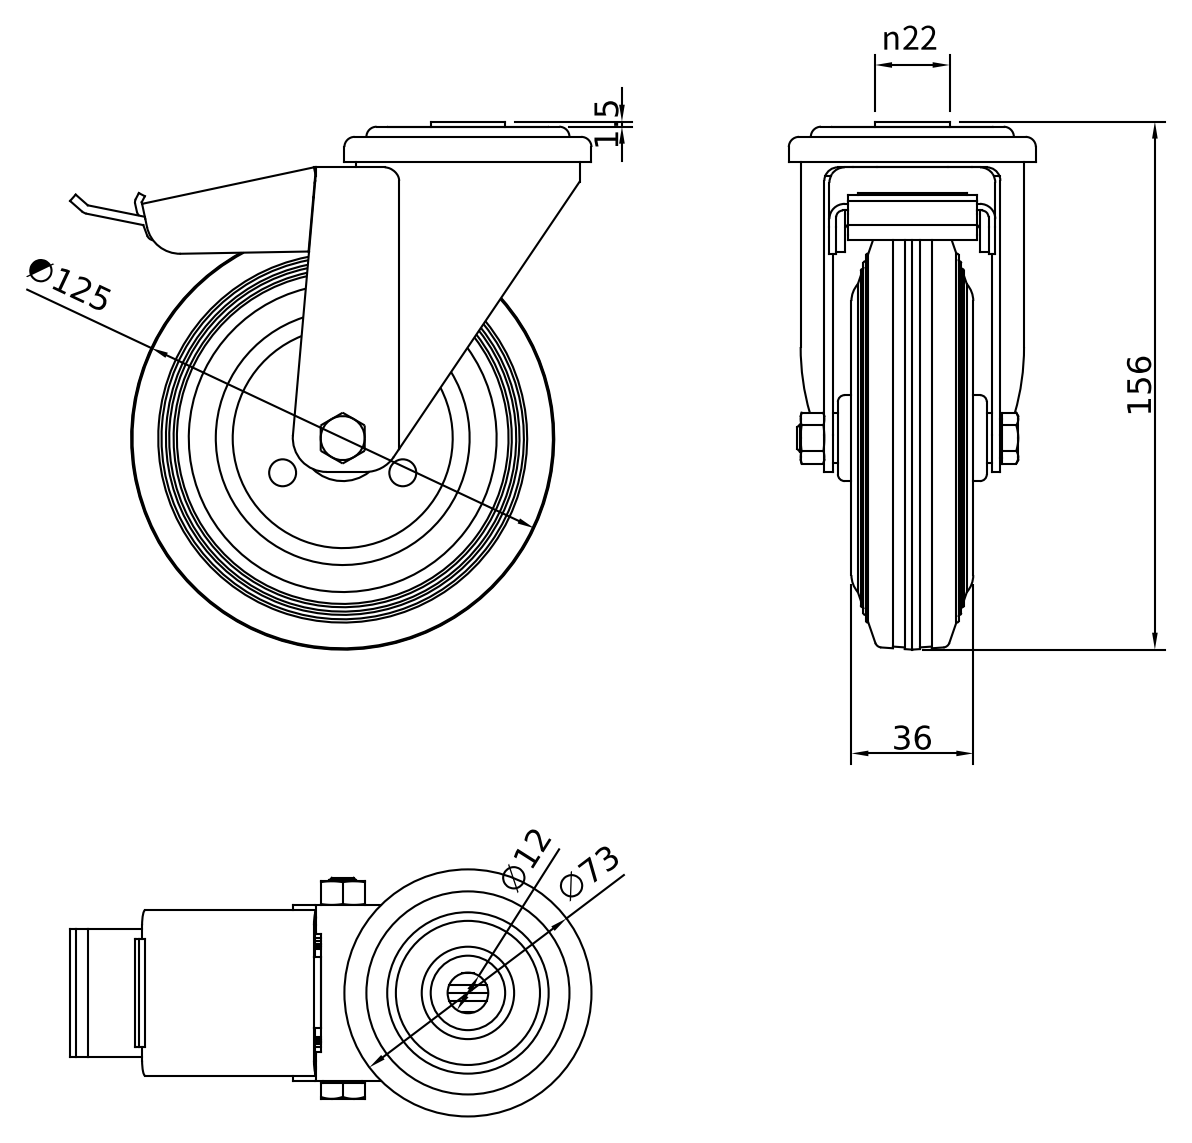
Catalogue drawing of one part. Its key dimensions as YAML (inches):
part_name: "CRUST0000185; 440000025371; 440000025372; 440000025373 (+3 more)"
step_written_by: "Autodesk Inventor 2022 (AUTOMOTIVE_DESIGN)"
units: inches
bodies: {solids: 6, faces: 228, planar: 117, cylindrical: 46, other: 65}
overall_size: [6.142, 6.065, 2.874]
volume: 24.18
surface_area: 155
round_holes:
  - {diameter: 0.262, count: 1}
  - {diameter: 0.315, count: 1}
  - {diameter: 0.472, count: 1}
  - {diameter: 0.591, count: 1}
  - {diameter: 0.61, count: 1}
  - {diameter: 0.709, count: 1}
  - {diameter: 2.441, count: 1}
  - {diameter: 2.559, count: 1}
round_bosses_or_shafts:
  - {diameter: 2.953, count: 1}
  - {diameter: 2.874, count: 1}
  - {diameter: 2.598, count: 1}
  - {diameter: 2.126, count: 1}
  - {diameter: 1, count: 1}
  - {diameter: 0.866, count: 1}
  - {diameter: 0.452, count: 1}
partial_cylinders:
  - {radius: 0.079, count: 5}
  - {radius: 0.394, count: 3}
  - {radius: 0.059, count: 2}
  - {radius: 0.157, count: 2}
  - {radius: 0.177, count: 2}
  - {radius: 0.087, count: 1}
  - {radius: 0.098, count: 1}
  - {radius: 0.118, count: 1}
face_to_face_distances: [0.098, 1.949, 0.079, 0.039, 1.85, 0.059, 0.138, 0.157, 0.976, 1.071]
